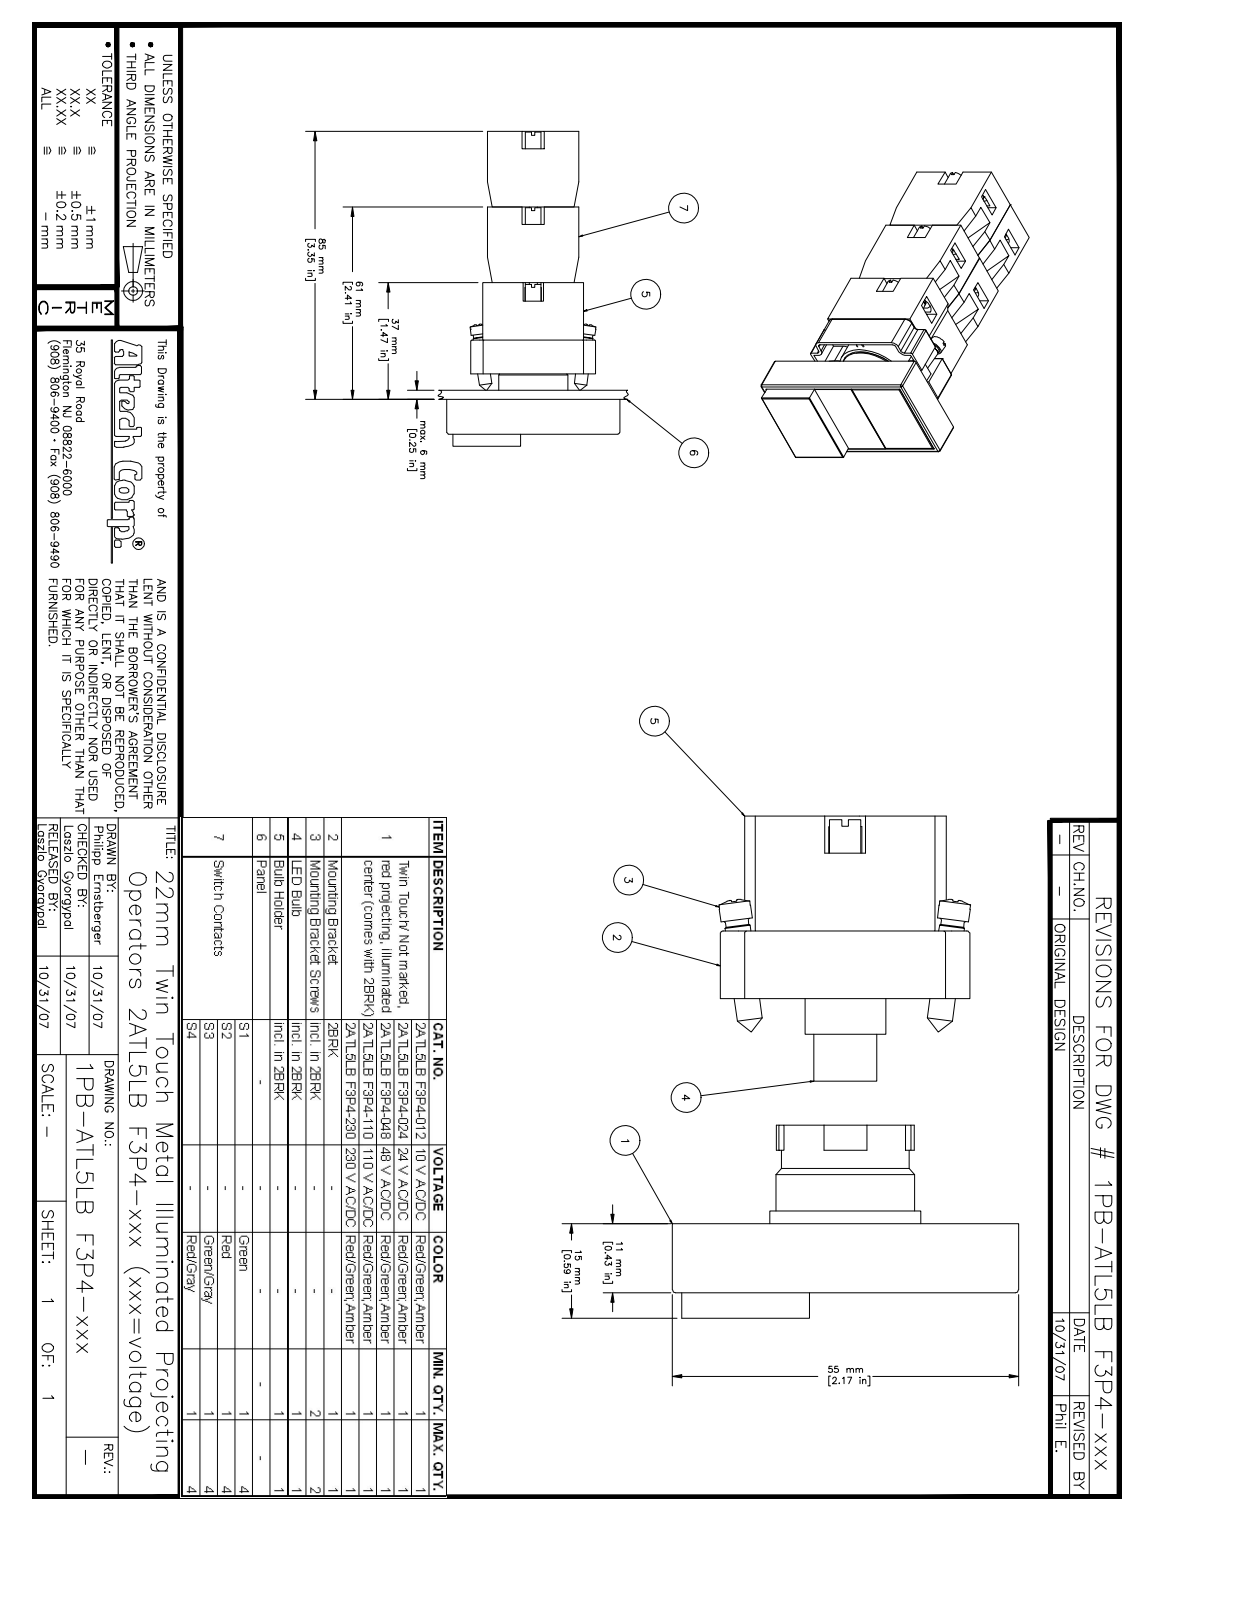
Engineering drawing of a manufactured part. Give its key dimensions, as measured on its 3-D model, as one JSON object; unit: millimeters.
{"part_name": "2ATL5LBF3P4-xxx_assembly; 2BRK; DIN 7985 (Z) M4x18-Z; S1 (+8 more)", "step_written_by": "Autodesk Inventor 2008 (AUTOMOTIVE_DESIGN)", "units": "millimeters", "bodies": {"solids": 28, "faces": 1119, "planar": 608, "cylindrical": 191, "other": 320}, "overall_size": [100.21, 60.45, 45], "volume_mm3": 81572, "surface_area_mm2": 50473, "round_holes": [[2.5, 5], [2.6, 2], [14, 1], [17.75, 1], [22, 1], [22.25, 1], [22.5, 1]], "round_bosses_or_shafts": [[3, 8], [2.75, 6], [5, 4], [1.5, 4], [4, 2], [3.65, 2], [24.25, 1], [24, 1]], "partial_cylinders_radius": [[1, 14], [0.5, 12], [0.25, 10], [0.2, 8], [0.72, 8], [2.25, 5], [0.8, 4], [1.8, 4]], "face_to_face_distances": [14.8, 14.7, 3, 24, 14.95, 15.05, 29.75, 1.7, 29.5, 15.91], "hole_center_spacings": [14.53, 6.52, 6.57, 13, 25.88, 26, 26.27, 29.07]}
